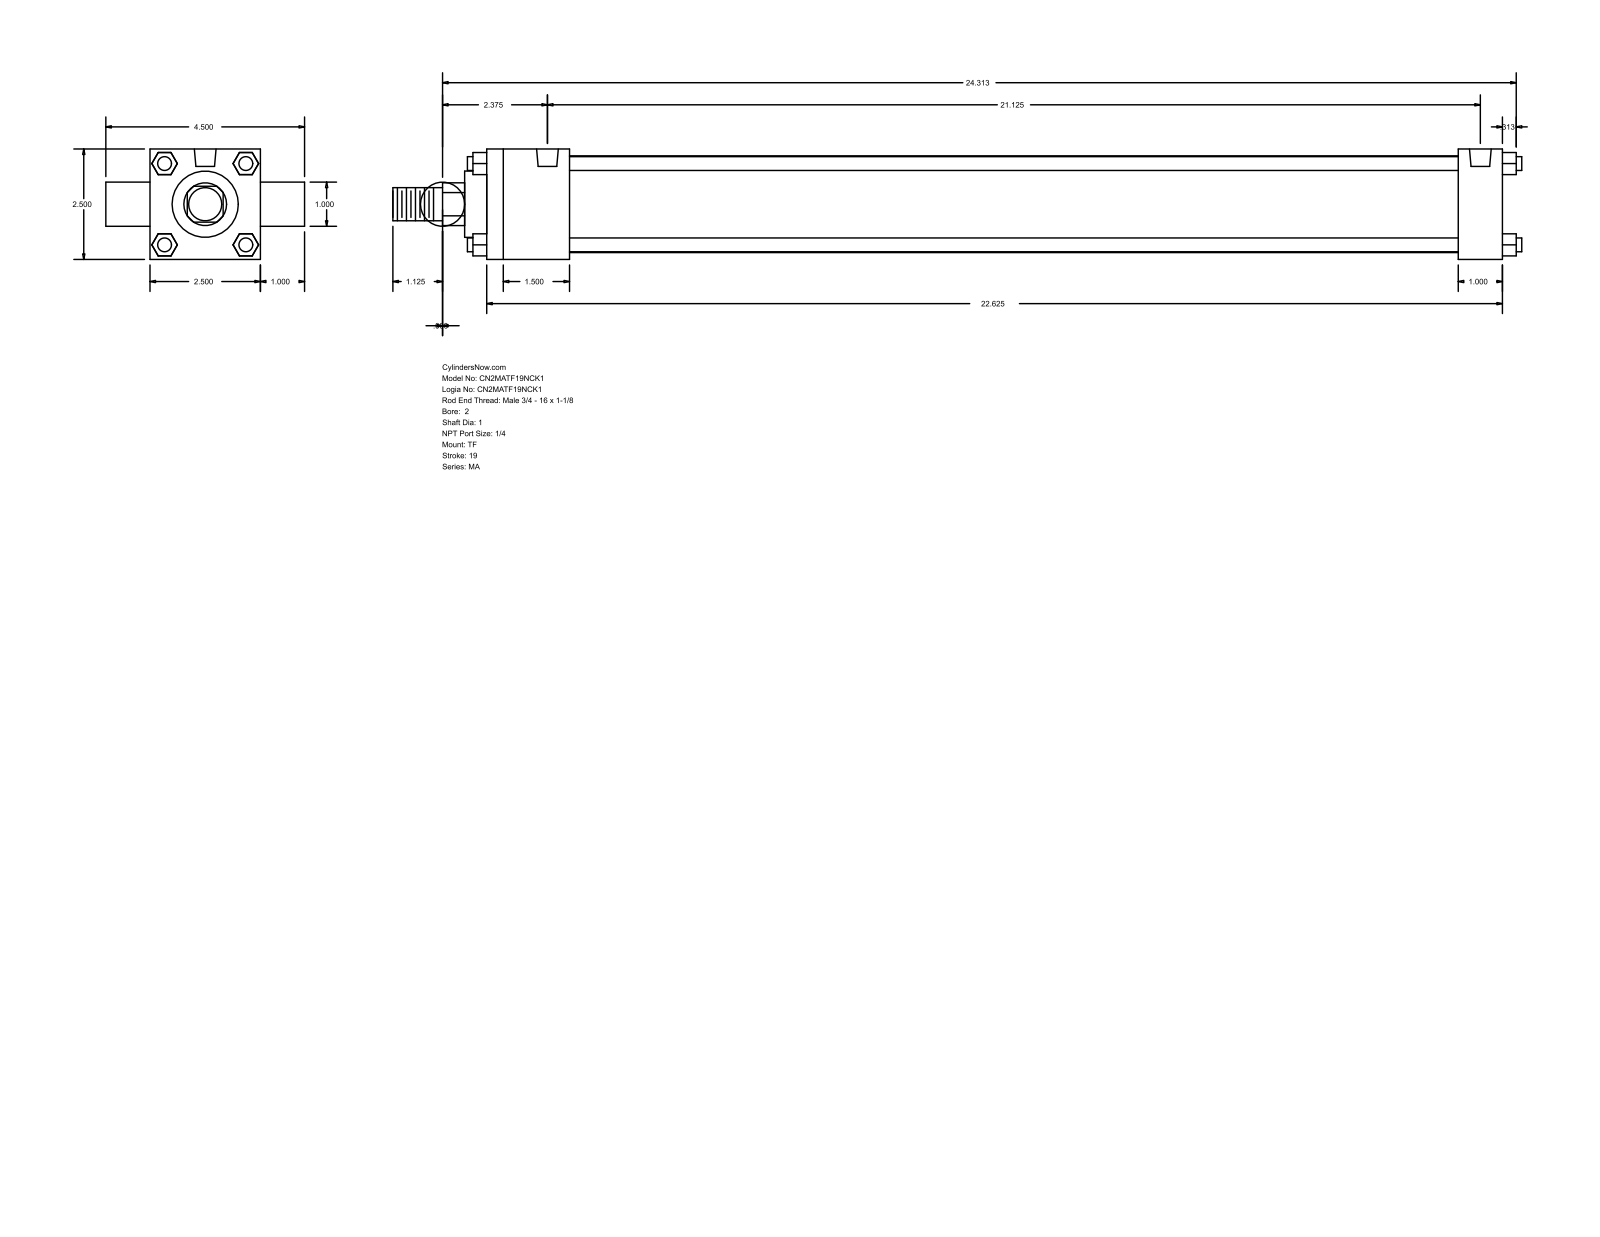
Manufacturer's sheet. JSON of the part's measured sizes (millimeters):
{"part_name": "MA_TF__0200_1", "step_written_by": "GSSL Pune (CONFIG_CONTROL_DESIGN)", "units": "millimeters", "bodies": {"solids": 0, "faces": 120, "planar": 92, "cylindrical": 28, "other": 0}, "overall_size": [649.29, 114.3, 63.5], "round_holes": [[7.94, 3], [12.49, 2]], "round_bosses_or_shafts": [[7.94, 4], [25.4, 2], [55.63, 1], [38.1, 1], [19.05, 1]], "partial_cylinders_radius": [[12.29, 1]], "face_to_face_distances": [63.5, 25.4, 584.2, 12.7, 47.63, 558.8, 511.17, 536.57, 88.9, 23.37], "hole_center_spacings": [536.57]}
